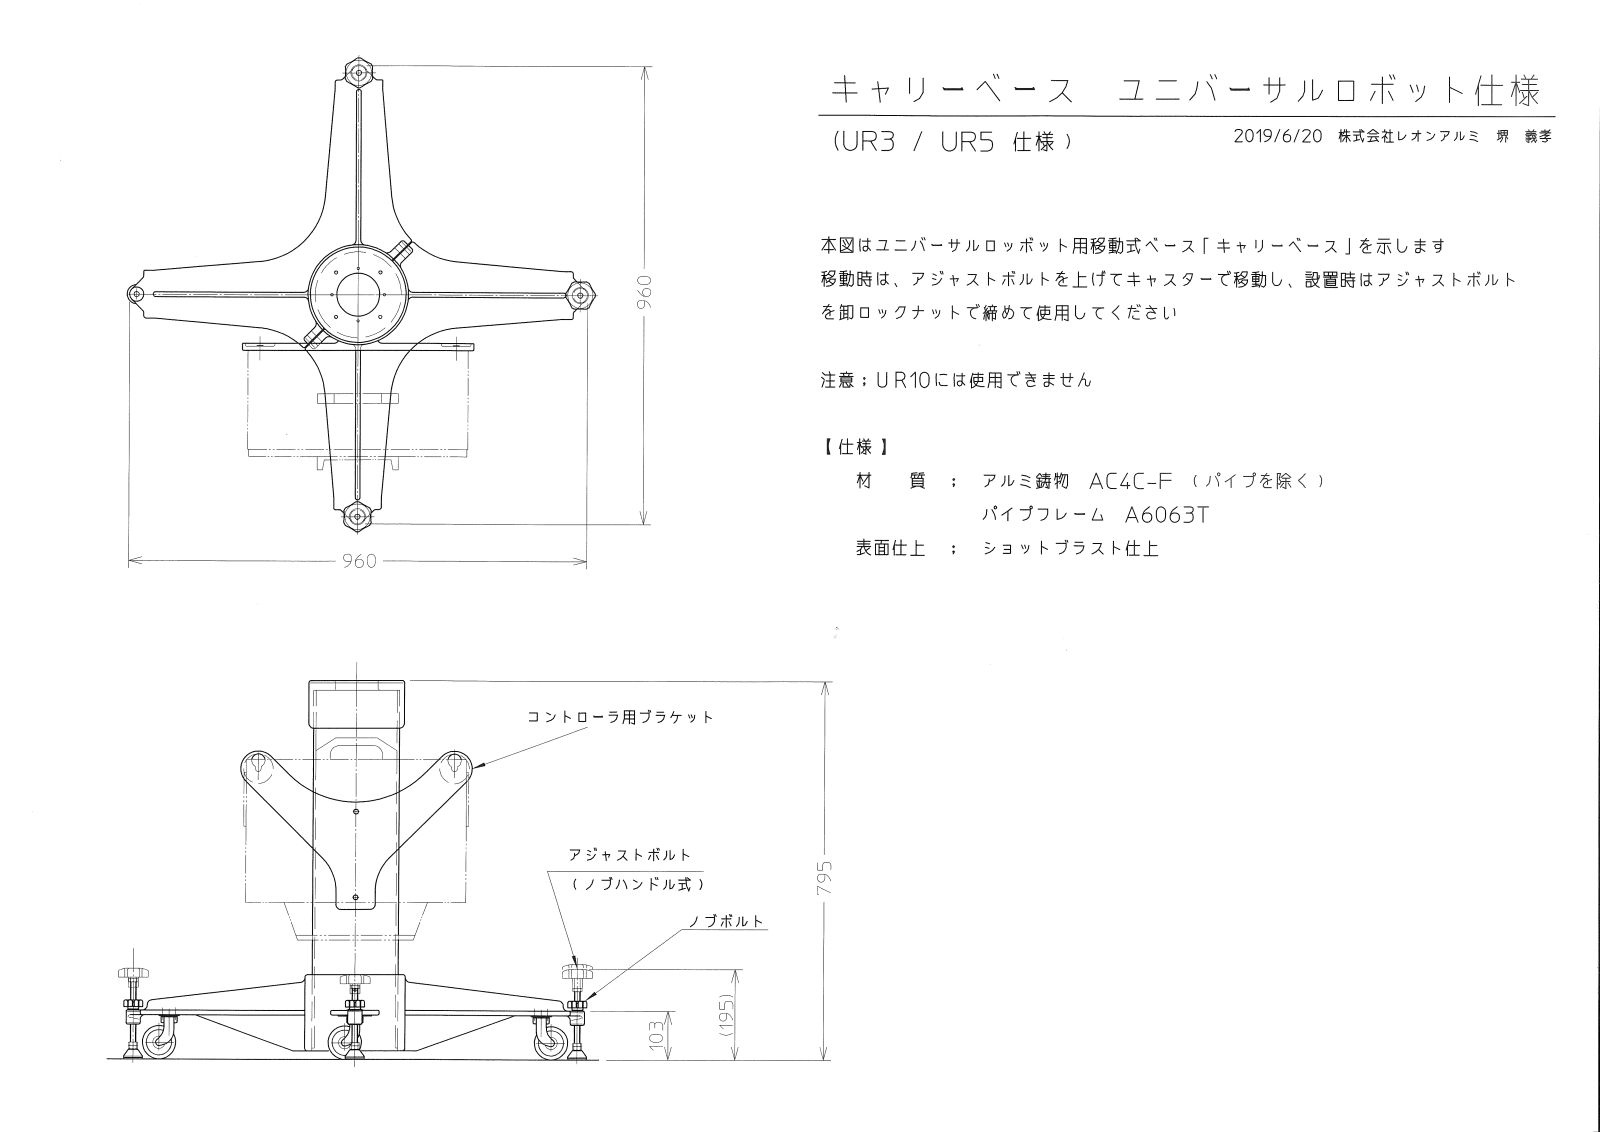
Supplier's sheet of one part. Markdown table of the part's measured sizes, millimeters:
| quantity | value |
| --- | --- |
| part name | パーツ55; パーツ196; パーツ259; パーツ348 (+7 more) |
| STEP written by | Spatial InterOp 3D (automotive_design) |
| units | millimeters |
| bodies | 82 solids, 5070 faces (2113 planar, 933 cylindrical, 2024 other) |
| overall size | 801.27 × 718.86 × 718.86 |
| volume | 10 190 000 mm³ |
| surface area | 2 265 000 mm² |
| round holes (diameter × count) | 6 × 18, 6.5 × 16, 13 × 11, 15 × 8, 52 × 8, 2 × 4, 4 × 4, 4.5 × 4, 12 × 4, 18 × 4, 22.9 × 4, 23 × 4 |
| round bosses / shafts (diameter × count) | 11.7 × 23, 12.7 × 16, 21 × 11, 30 × 10, 26 × 10, 12 × 6, 40 × 4, 39 × 4 |
| partial cylindrical surfaces (radius × count) | 2 × 88, 0.5 × 64, 10 × 56, 1.8 × 48, 5 × 44, 1.5 × 41, 6 × 34, 1.3 × 8 |
| main face-to-face distances | 10, 15, 20, 705, 685, 675, 695, 75, 85, 2 |
| hole center spacings | 31.7, 744.24, 505.97, 546.71, 772.81, 758, 31.71, 365.8 |
